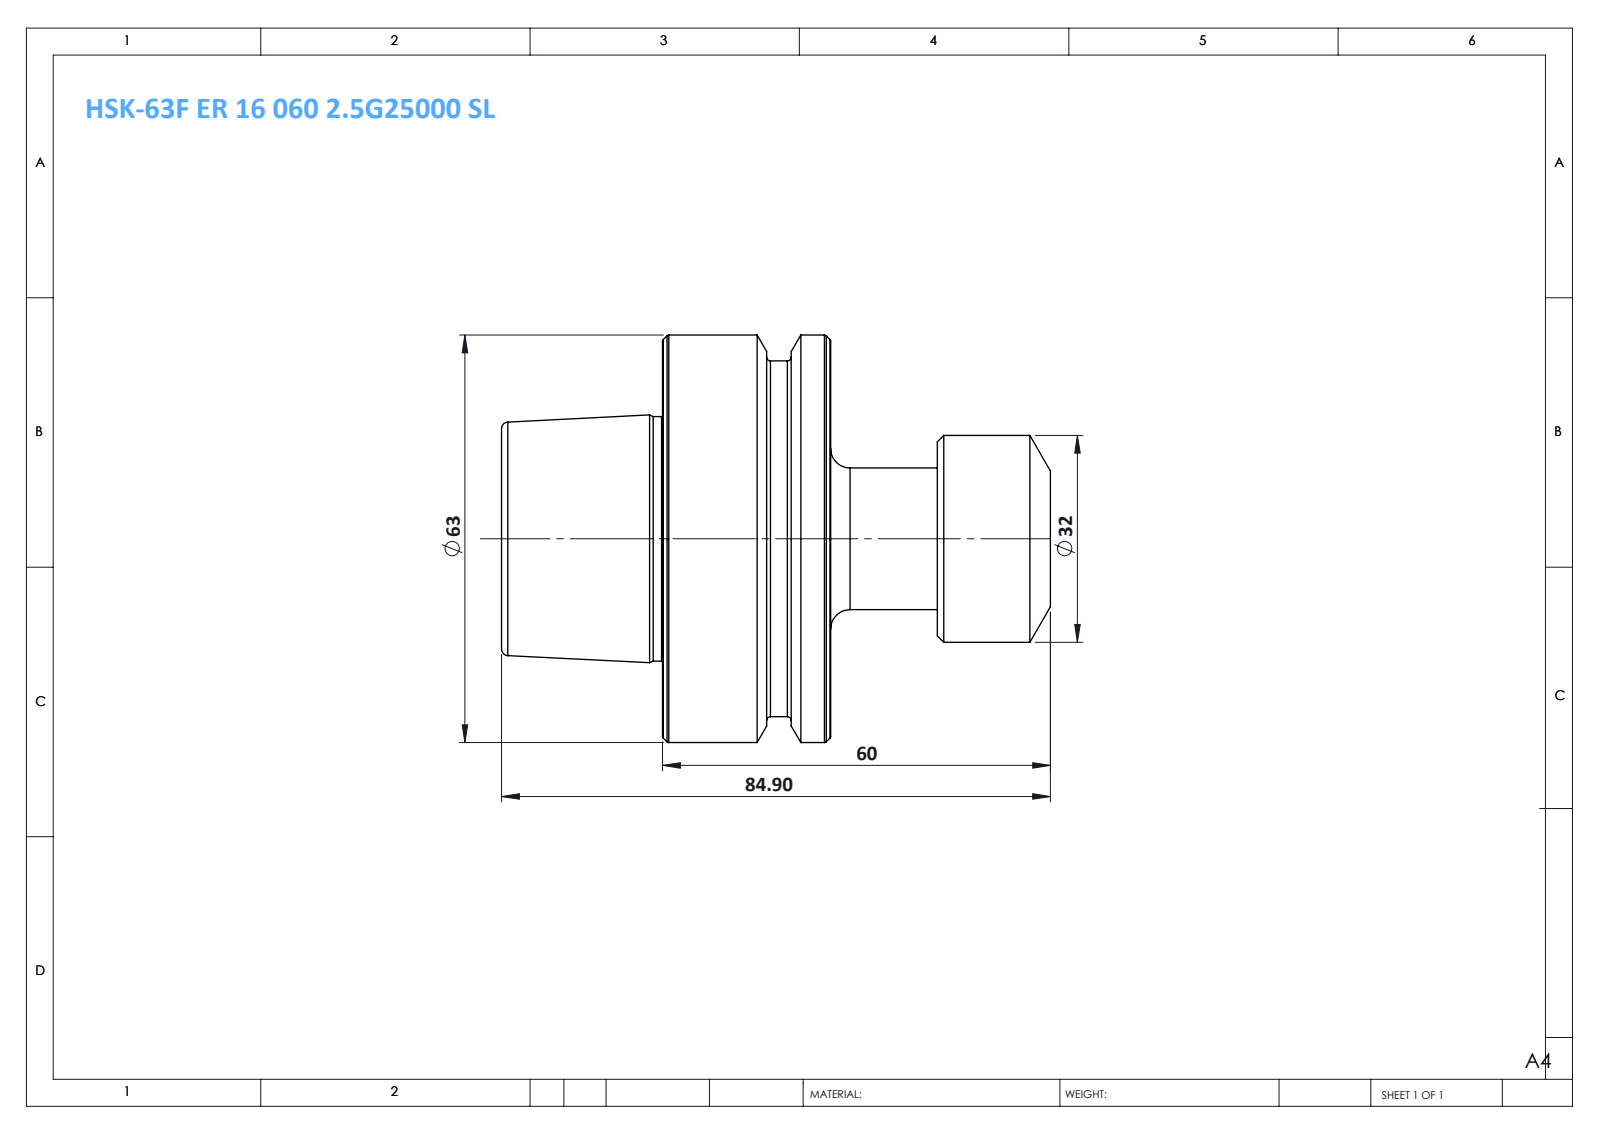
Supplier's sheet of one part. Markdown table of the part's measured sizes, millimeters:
| quantity | value |
| --- | --- |
| part name | HSK-63F ER 16 060 2.5G25000 SL |
| STEP written by | SolidWorks 2014 (CONFIG_CONTROL_DESIGN) |
| units | millimeters |
| bodies | 1 solid, 55 faces (7 planar, 12 cylindrical, 36 other) |
| overall size | 84.9 × 63 × 63 |
| volume | 124 054 mm³ |
| surface area | 18 187 mm² |
| round bosses / shafts (diameter × count) | 63 × 1, 55 × 1, 37.8 × 1, 32 × 1, 21.9 × 1 |
| main face-to-face distances | 26, 50.9, 24.9, 34, 60, 84.9, 17.5, 16.5, 42.5, 67.4 |
